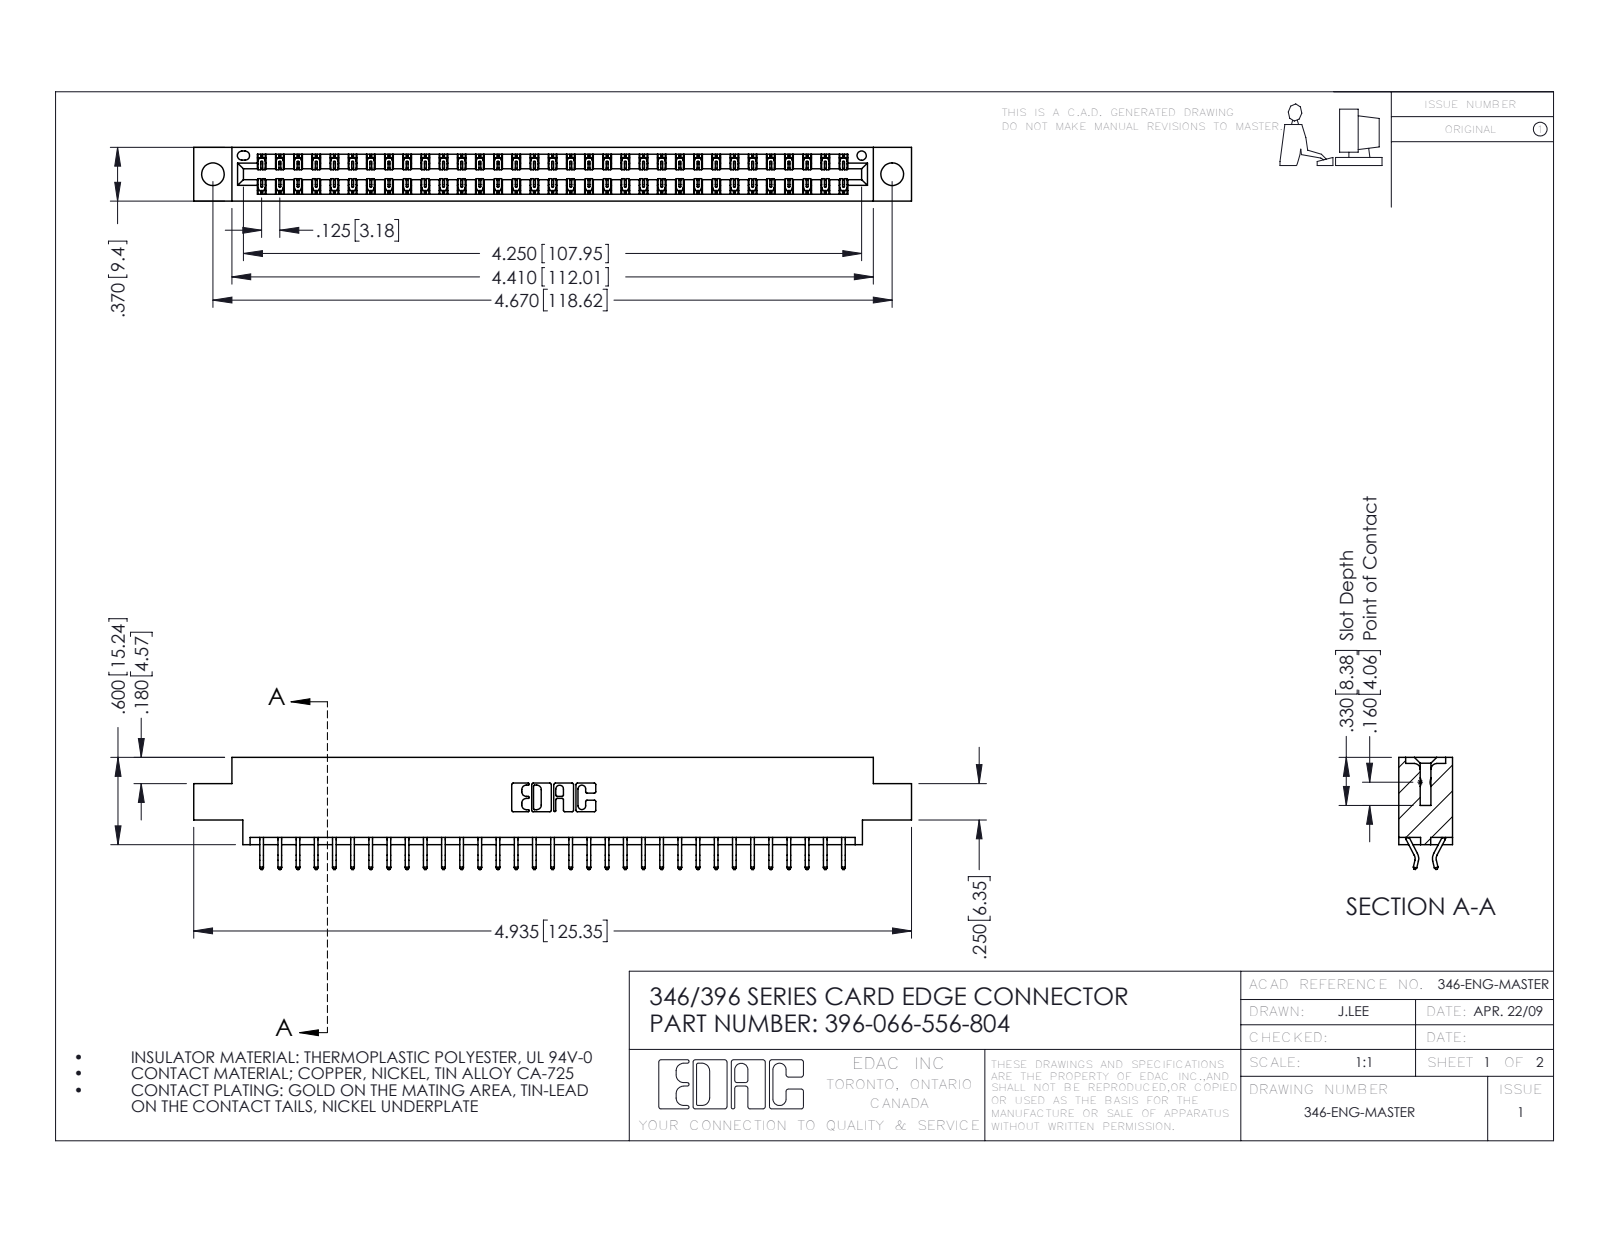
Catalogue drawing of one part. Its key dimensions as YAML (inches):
part_name: "346 Part_0.170 Offset - 0.156 Dia-TH; 396-066-556-804; 345-292-001_556 Tail"
step_written_by: "SolidWorks 2016 (CONFIG_CONTROL_DESIGN)"
units: inches
bodies: {solids: 67, faces: 3954, planar: 2654, cylindrical: 1300, other: 0}
overall_size: [4.935, 0.77, 0.37]
volume: 0.727
surface_area: 25.05
round_holes:
  - {diameter: 0.156, count: 2}
  - {diameter: 0.064, count: 1}
partial_cylinders:
  - {radius: 0.006, count: 99}
  - {radius: 0.01, count: 22}
  - {radius: 0.007, count: 6}
  - {radius: 0.031, count: 6}
  - {radius: 0.026, count: 3}
  - {radius: 0.01, count: 2}
  - {radius: 0.014, count: 2}
  - {radius: 0.022, count: 2}
face_to_face_distances: [0.048, 0.322, 0.37, 0.25, 0.025, 0.072, 0.298, 0.275, 0.148, 0.222]
hole_center_spacings: [0.246, 4.462, 4.67]
